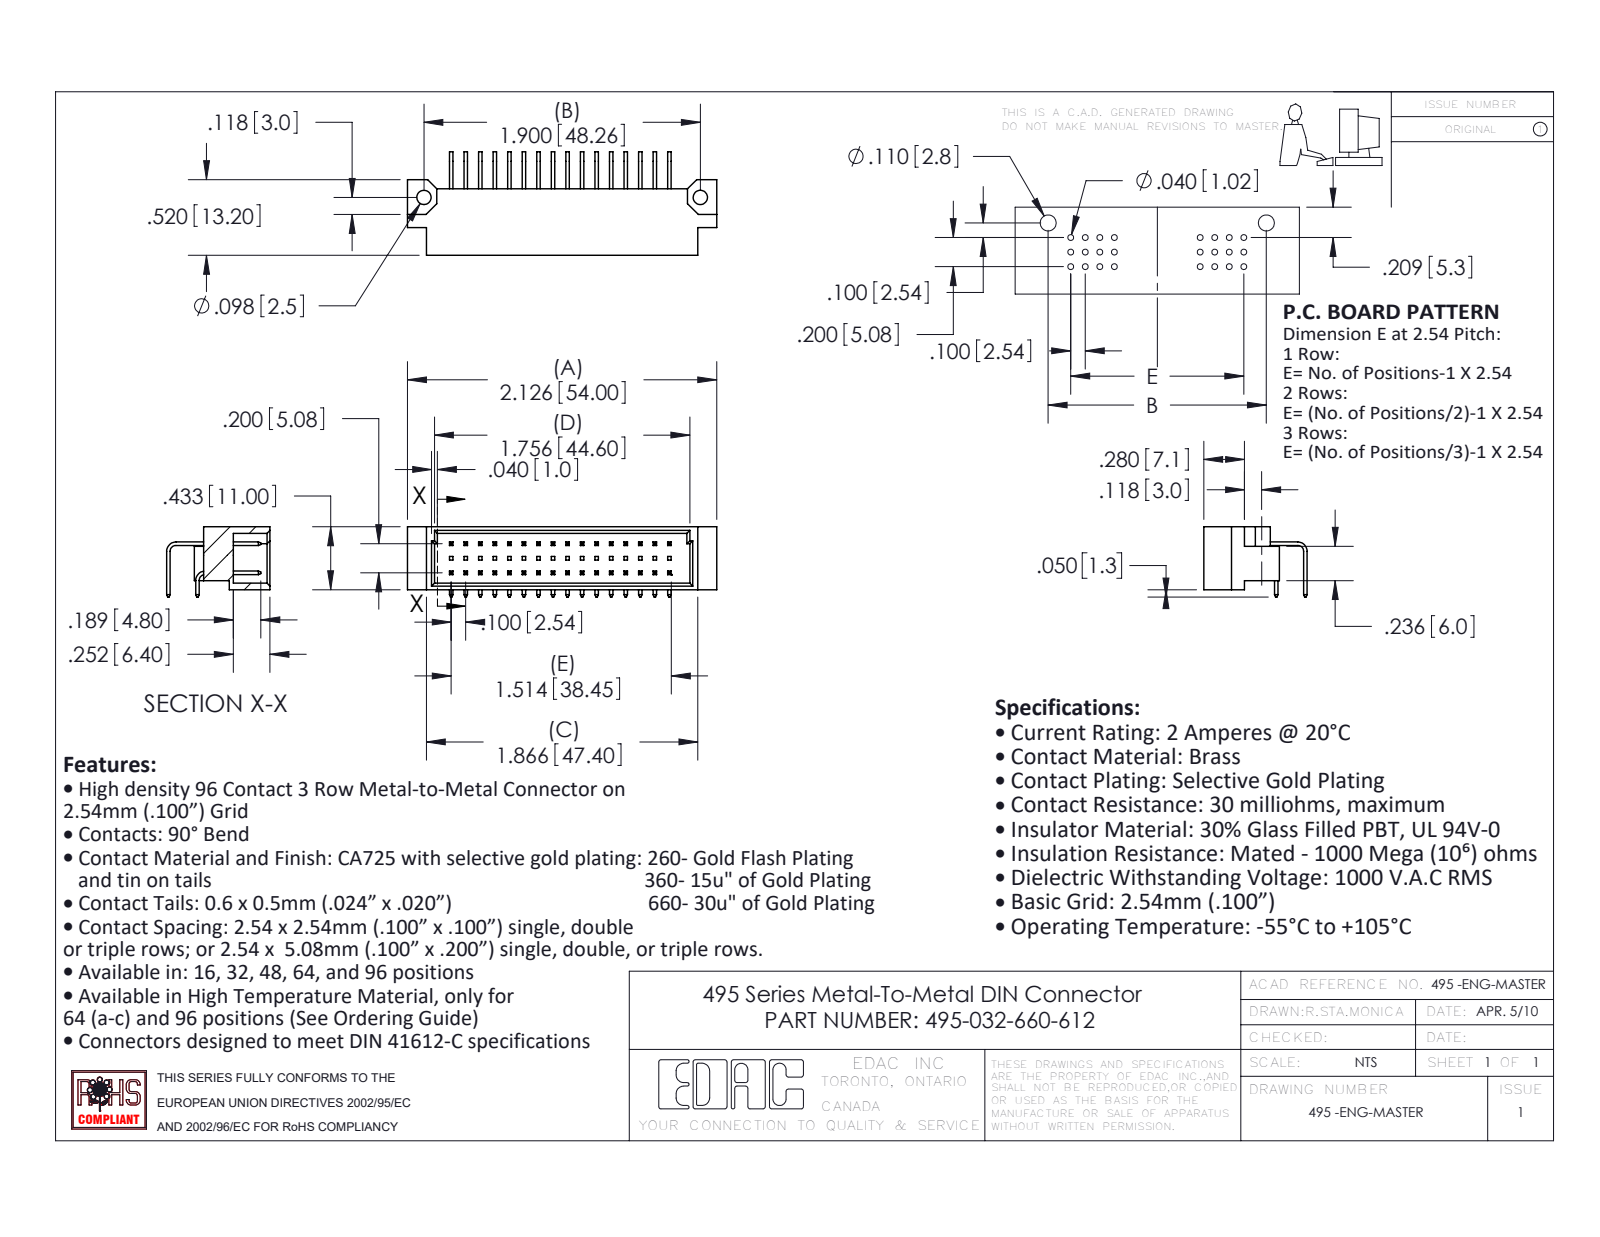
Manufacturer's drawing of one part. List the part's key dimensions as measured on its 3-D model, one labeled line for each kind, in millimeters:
Part name (STEP PRODUCT): 495-290-1; 495-032-660-612; 495-290-3; 495 Part_48
STEP written by: SolidWorks 2020 (AUTOMOTIVE_DESIGN)
Units: millimetres
Bodies: 33 solids, 818 faces (750 planar, 68 cylindrical, 0 other)
Overall size (bounding box): 54 × 18.05 × 12.27
Volume: 3 680 mm³ · Surface area: 5 496 mm²
Round holes (diameter × count): ⌀2.49 ×2
Partial cylindrical surfaces — rounded edges, fillets, slot ends (radius × count): R1.02 ×2, R1.65 ×2
Main face-to-face distances: 5.08, 2.54, 1.14, 9.86, 0.61, 5.2, 11, 7.62, 1.6, 10.16
Hole centre spacings: 48.26
